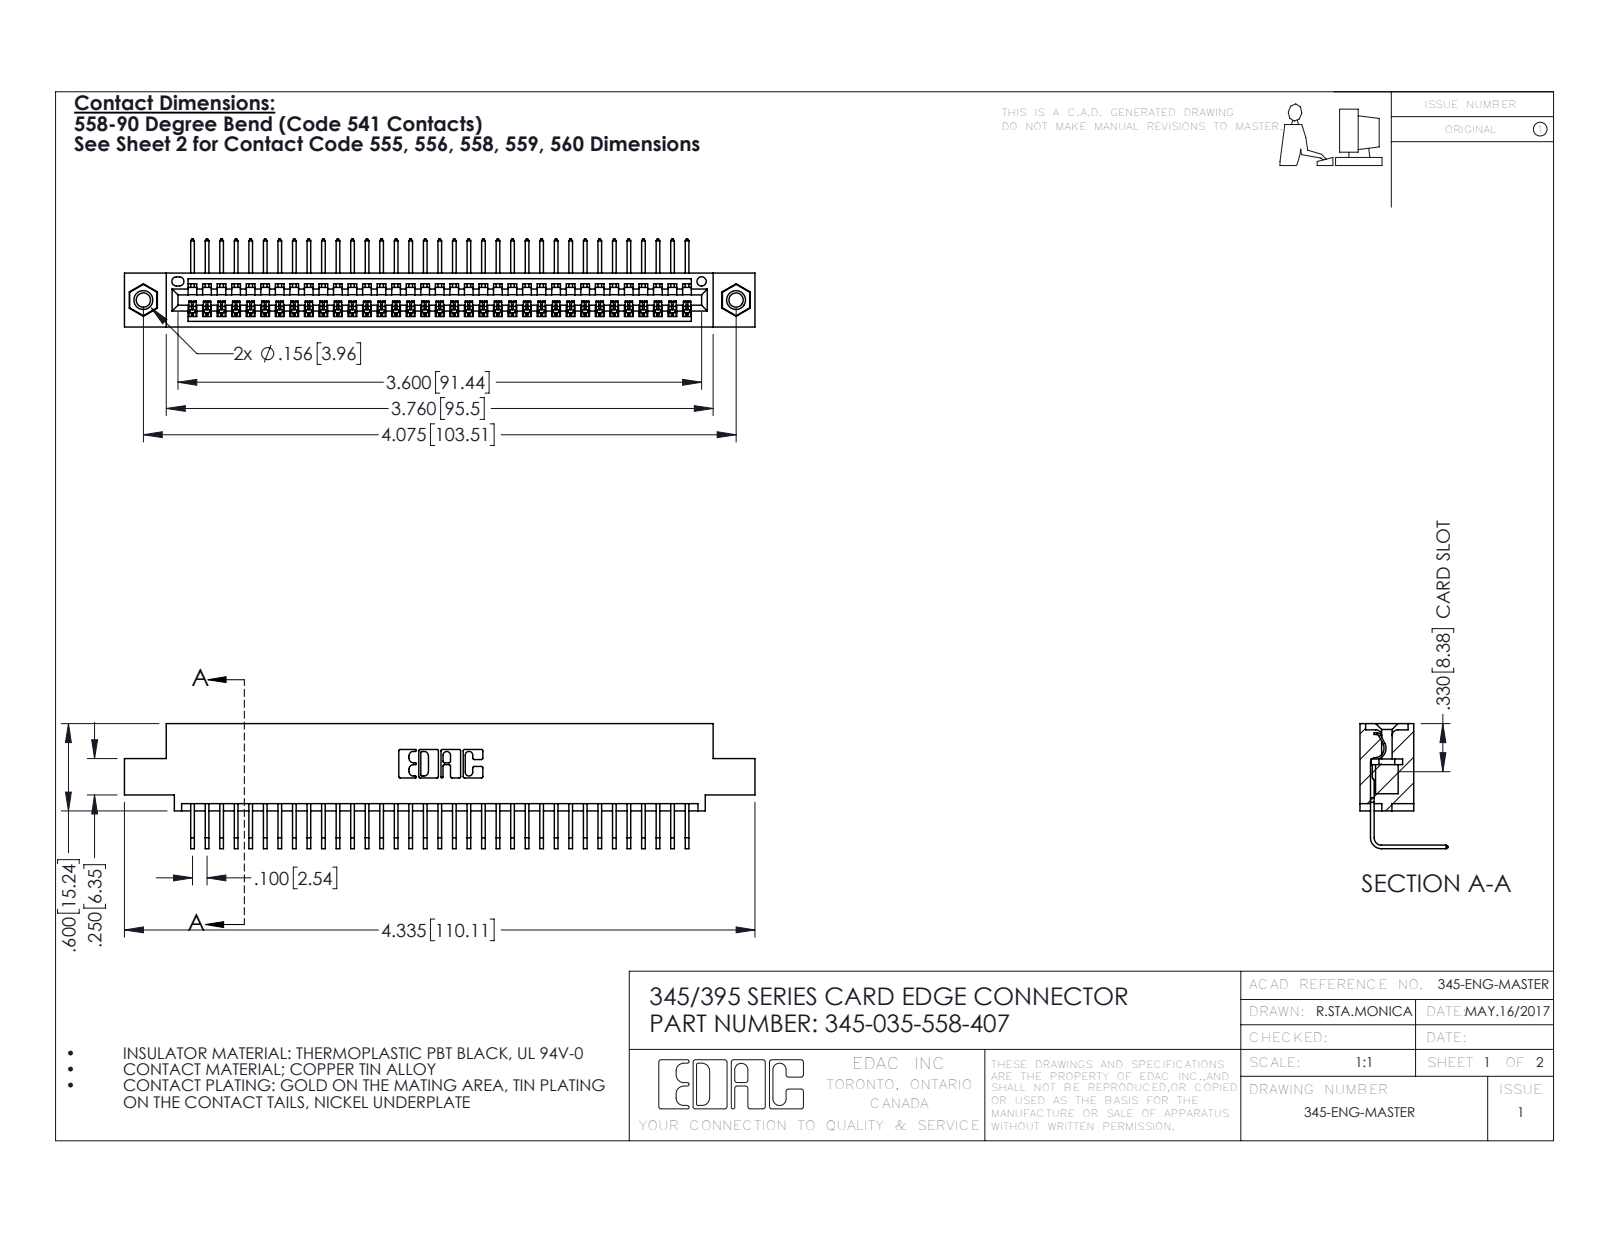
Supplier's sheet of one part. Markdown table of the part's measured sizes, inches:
| quantity | value |
| --- | --- |
| part name | 345-292-001_558 Tail - 2; 345-250-001_345-250-005-103; 345-035-558-407; 345 Part_0.110 Offset - 0.156 Dia-TI |
| STEP written by | SolidWorks 2016 (CONFIG_CONTROL_DESIGN) |
| units | inches |
| bodies | 38 solids, 2290 faces (1586 planar, 688 cylindrical, 16 other) |
| overall size | 4.335 × 0.859 × 0.605 |
| volume | 0.637 in³ |
| surface area | 22.58 in² |
| round holes (diameter × count) | 0.098 × 2, 0.125 × 2, 0.156 × 2, 0.064 × 1 |
| round bosses / shafts (diameter × count) | 0.155 × 2 |
| partial cylindrical surfaces (radius × count) | 0.006 × 70, 0.01 × 22, 0.007 × 6, 0.031 × 6, 0.026 × 3, 0.031 × 2, 0.04 × 2, 0.014 × 1 |
| main face-to-face distances | 0.072, 0.298, 0.37, 0.2, 0.098, 0.272, 0.025, 0.225, 0.149, 0.072 |
| hole center spacings | 0.27, 3.839, 4.075 |
